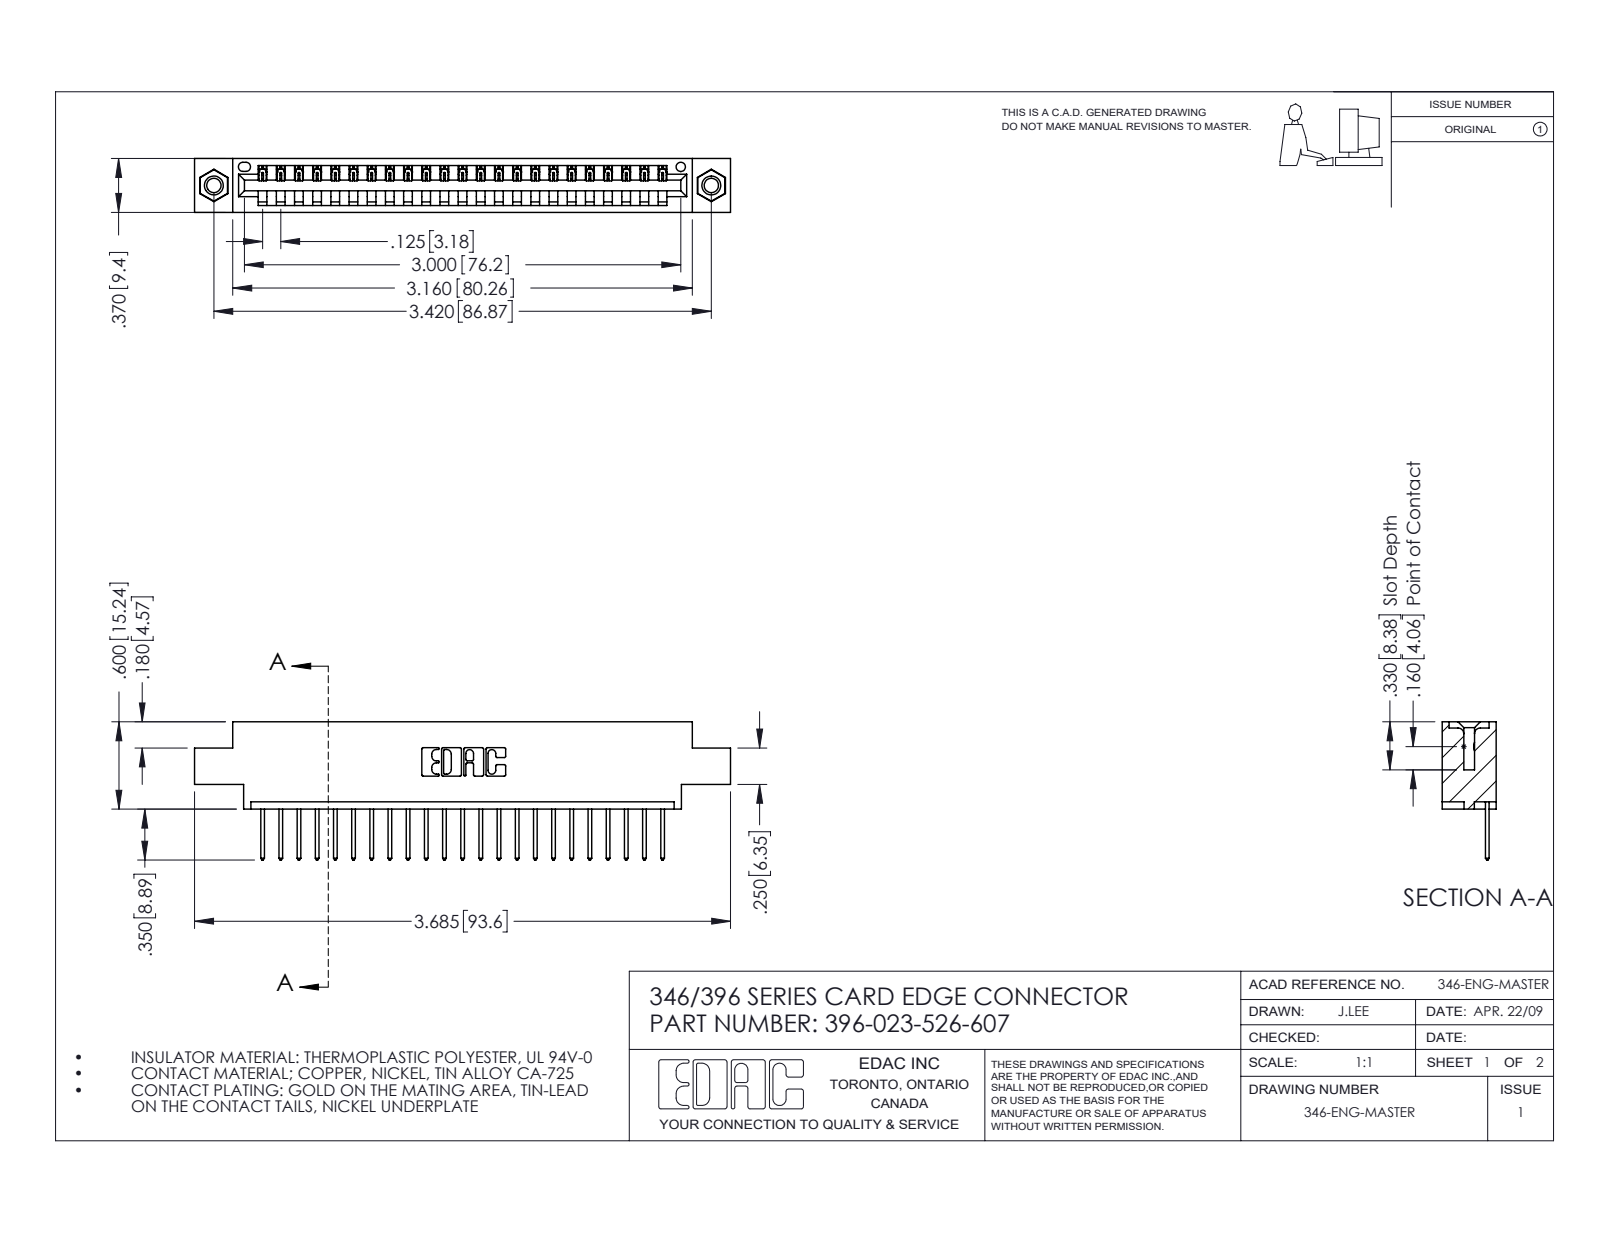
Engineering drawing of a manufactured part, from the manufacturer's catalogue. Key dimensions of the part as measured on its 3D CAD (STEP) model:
Part name (STEP PRODUCT): 345-250-001_345-250-005-103; 396-023-526-607; 346 Part_0.170 Offset - 0.156 Dia-TI; 345-292-001_345-293-126
STEP written by: SolidWorks 2016 (CONFIG_CONTROL_DESIGN)
Units: inches
Bodies: 26 solids, 1520 faces (1032 planar, 472 cylindrical, 16 other)
Overall size (bounding box): 3.685 × 0.95 × 0.37
Volume: 0.527 in³ · Surface area: 16.69 in²
Round holes (diameter × count): ⌀0.098 ×2, ⌀0.125 ×2, ⌀0.156 ×2, ⌀0.064 ×1
Round bosses / shafts (diameter × count): ⌀0.155 ×2
Partial cylindrical surfaces — rounded edges, fillets, slot ends (radius × count): R0.006 ×46, R0.01 ×46, R0.01 ×22, R0.007 ×6, R0.031 ×6, R0.026 ×3, R0.031 ×2, R0.04 ×2
Main face-to-face distances: 0.048, 0.322, 0.37, 0.25, 0.072, 0.298, 0.025, 0.222, 0.148, 0.1
Hole centre spacings: 0.246, 3.212, 3.42
